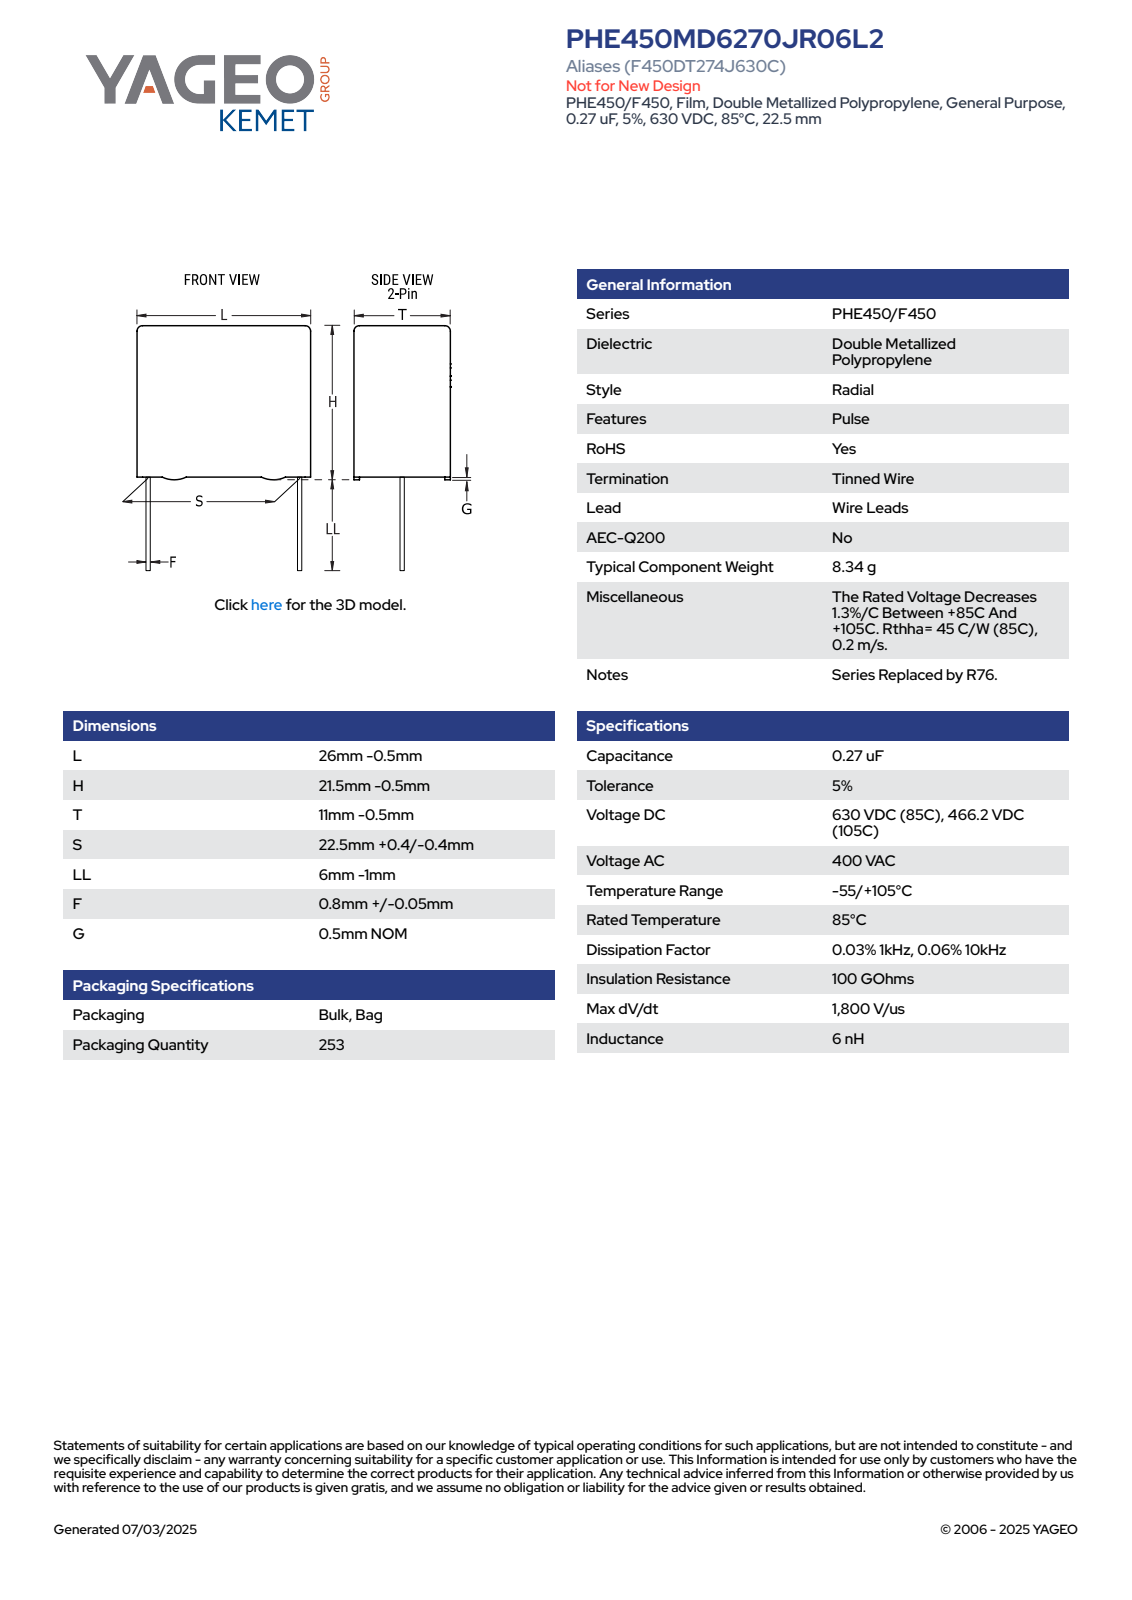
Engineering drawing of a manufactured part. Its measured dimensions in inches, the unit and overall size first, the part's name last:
Units: inches
Overall size (bounding box): 1.024 × 1.004 × 0.414
Round bosses / shafts (diameter × count): ⌀0.033 ×2
Partial cylindrical surfaces — rounded edges, fillets, slot ends (radius × count): R0.02 ×4
Main face-to-face distances: 0.413, 0.807, 1.004, 0.414, 0.02, 0.827, 0.024, 0.39, 0.366, 0.39
Volume: 0.335 in³ · Surface area: 3.275 in²
Bodies: 4 solids, 89 faces (81 planar, 8 cylindrical, 0 other)
Part name (STEP PRODUCT): CFR_RBG_26X21.5X11_L25.5H21T10.5S22.5LL5F0.85G0.5
STEP written by: SolidWorks 2021 (AUTOMOTIVE_DESIGN)
